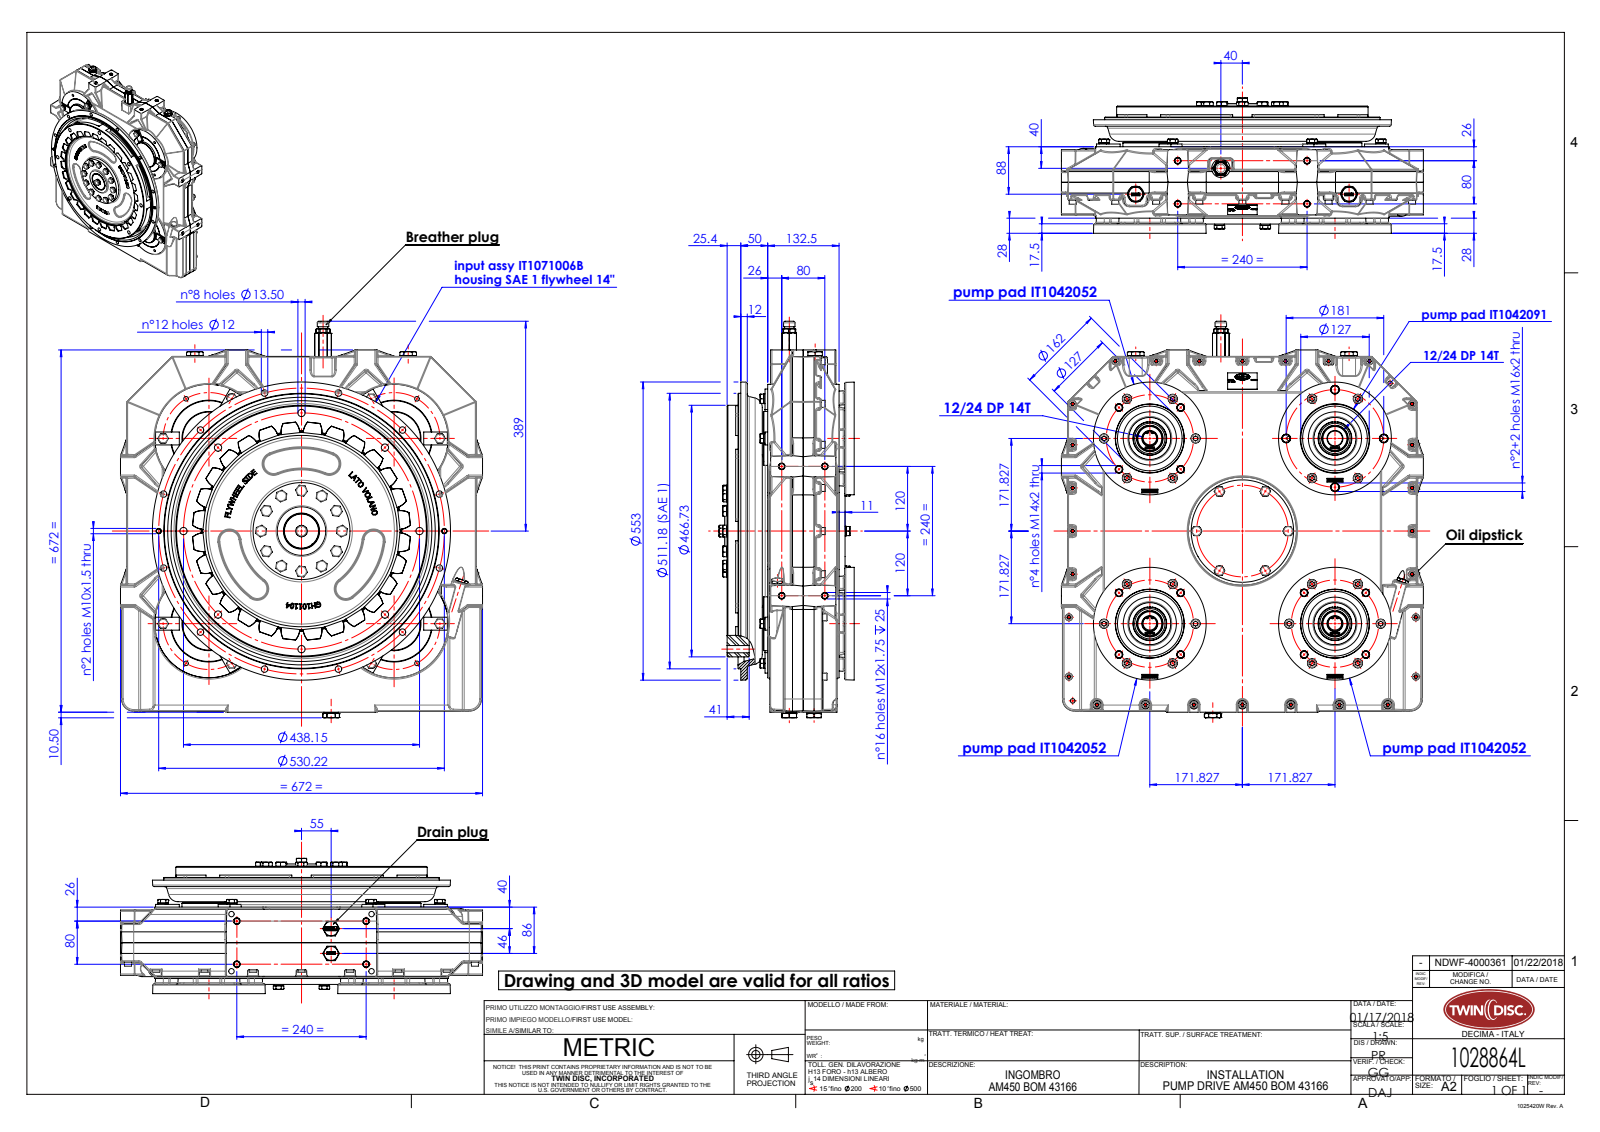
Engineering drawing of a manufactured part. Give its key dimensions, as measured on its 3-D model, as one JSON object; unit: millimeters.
{"part_name": "IT4588040_rev00-installation; IT2021216_rev03-installation; IT1042052_rev00-installation; ITam450-002_rev00-installation (+8 more)", "step_written_by": "SolidWorks 2015 (AUTOMOTIVE_DESIGN)", "units": "millimeters", "bodies": {"solids": 72, "faces": 10709, "planar": 5097, "cylindrical": 2654, "other": 2958}, "overall_size": [735.8, 672.41, 251], "volume_mm3": 12060000, "surface_area_mm2": 5422000, "round_holes": [[8.5, 70], [12, 33], [10.2, 29], [11, 29], [17, 22], [13, 19], [14, 17], [10, 12], [16, 11], [13.5, 8], [12.2, 7], [2, 6]], "round_bosses_or_shafts": [[10, 31], [13, 28], [8, 28], [16, 22], [18, 19], [12, 19], [16.2, 15], [18.1, 14]], "partial_cylinders_radius": [[2.5, 324], [0.75, 112], [2, 106], [0.45, 58], [34, 56], [34.2, 56], [3, 48], [1.5, 27]], "face_to_face_distances": [10, 128.5, 4, 62.5, 66, 66.5, 28, 20, 148.5, 86], "hole_center_spacings": [85, 120, 178.39, 243, 254.31, 57.4, 75, 106.89]}
